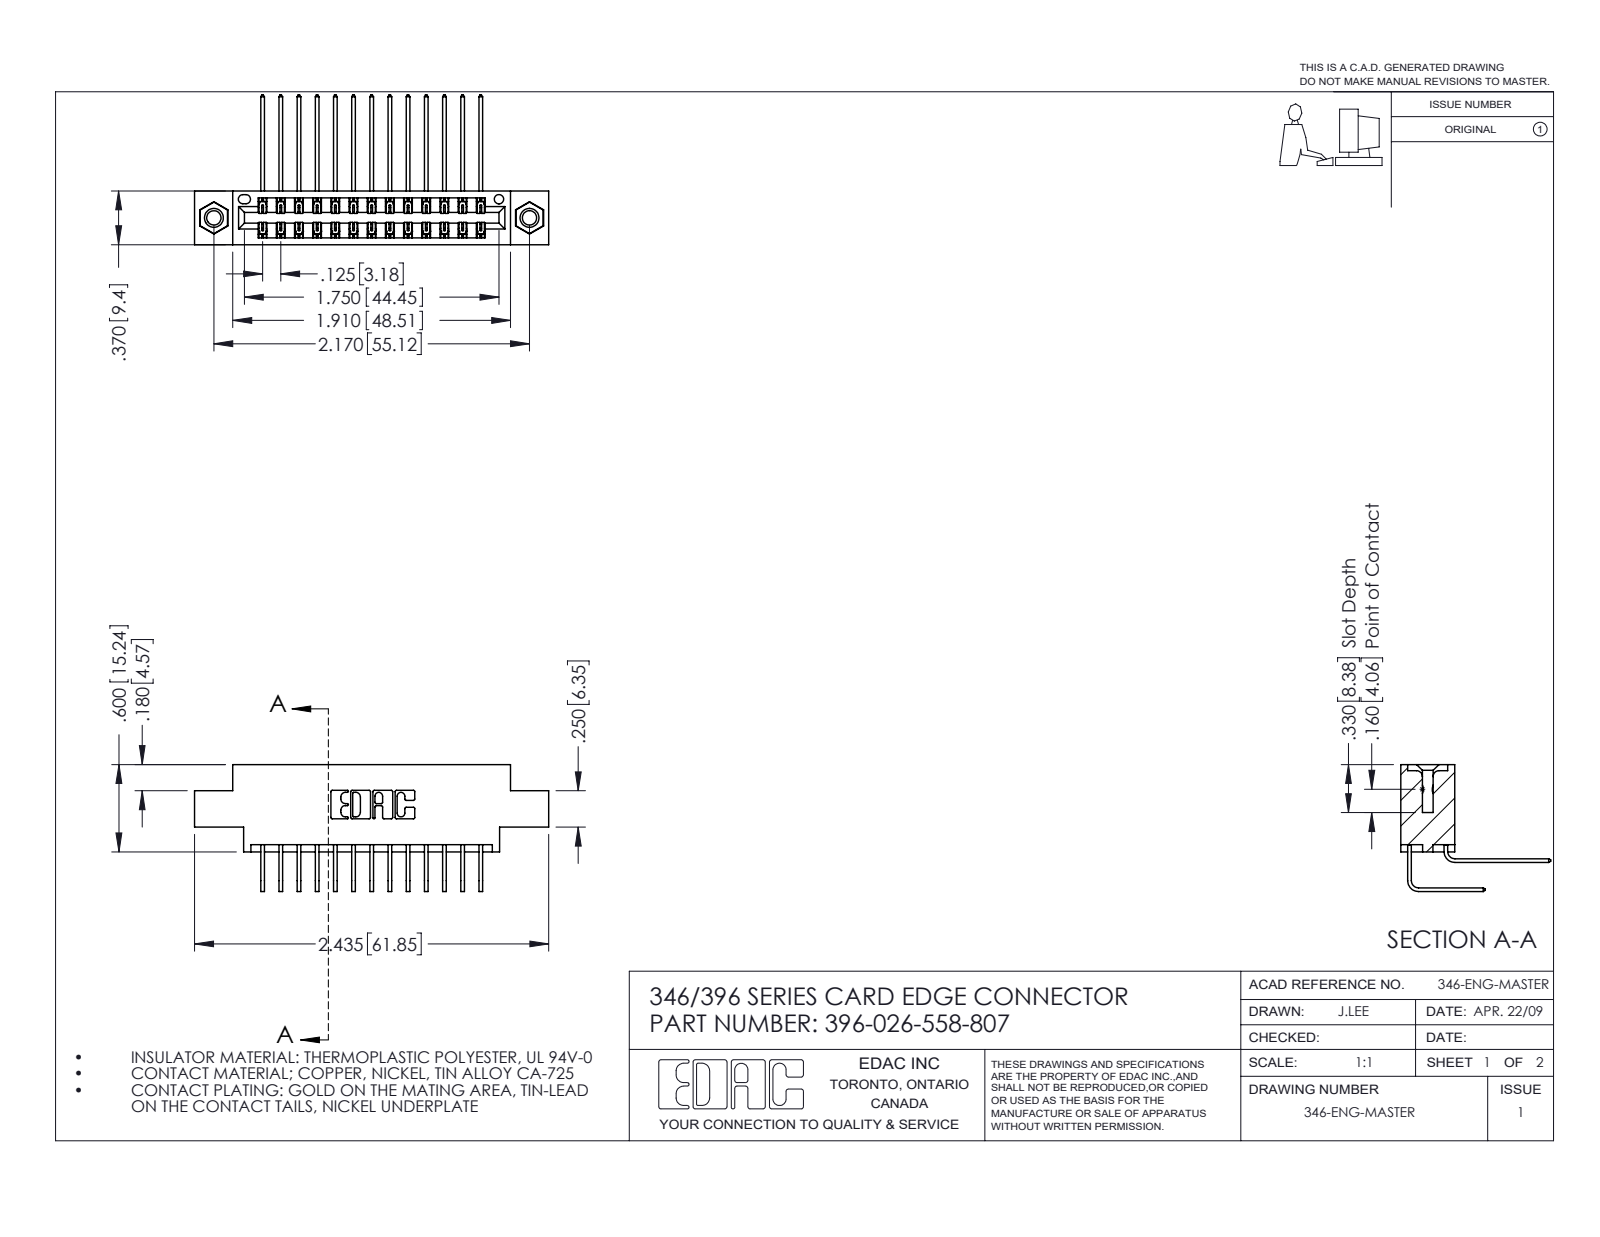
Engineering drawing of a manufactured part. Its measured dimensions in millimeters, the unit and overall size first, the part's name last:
Units: millimetres
Overall size (bounding box): 61.8 × 26.2 × 22.2
Round holes (diameter × count): ⌀2.5 ×2, ⌀3.2 ×2, ⌀4 ×2, ⌀1.6 ×1
Round bosses / shafts (diameter × count): ⌀3.9 ×2
Partial cylindrical surfaces — rounded edges, fillets, slot ends (radius × count): R0.2 ×39, R0.3 ×22, R0.2 ×6, R0.8 ×6, R0.7 ×3, R0.4 ×2, R0.6 ×2, R0.6 ×2
Main face-to-face distances: 1.2, 8.2, 6.4, 9.4, 0.6, 1.8, 7.6, 5.6, 7, 3.8
Hole centre spacings: 6.2, 49.9, 55.1
Volume: 5 780 mm³ · Surface area: 8 432 mm²
Bodies: 29 solids, 1590 faces (1074 planar, 500 cylindrical, 16 other)
Part name (STEP PRODUCT): 346 Part_0.170 Offset - 0.156 Dia-TI; 345-292-001_558 Tail - 2; 396-026-558-807; 345-292-001_558 559 Tail - 1 (+1 more)
STEP written by: SolidWorks 2016 (CONFIG_CONTROL_DESIGN)
